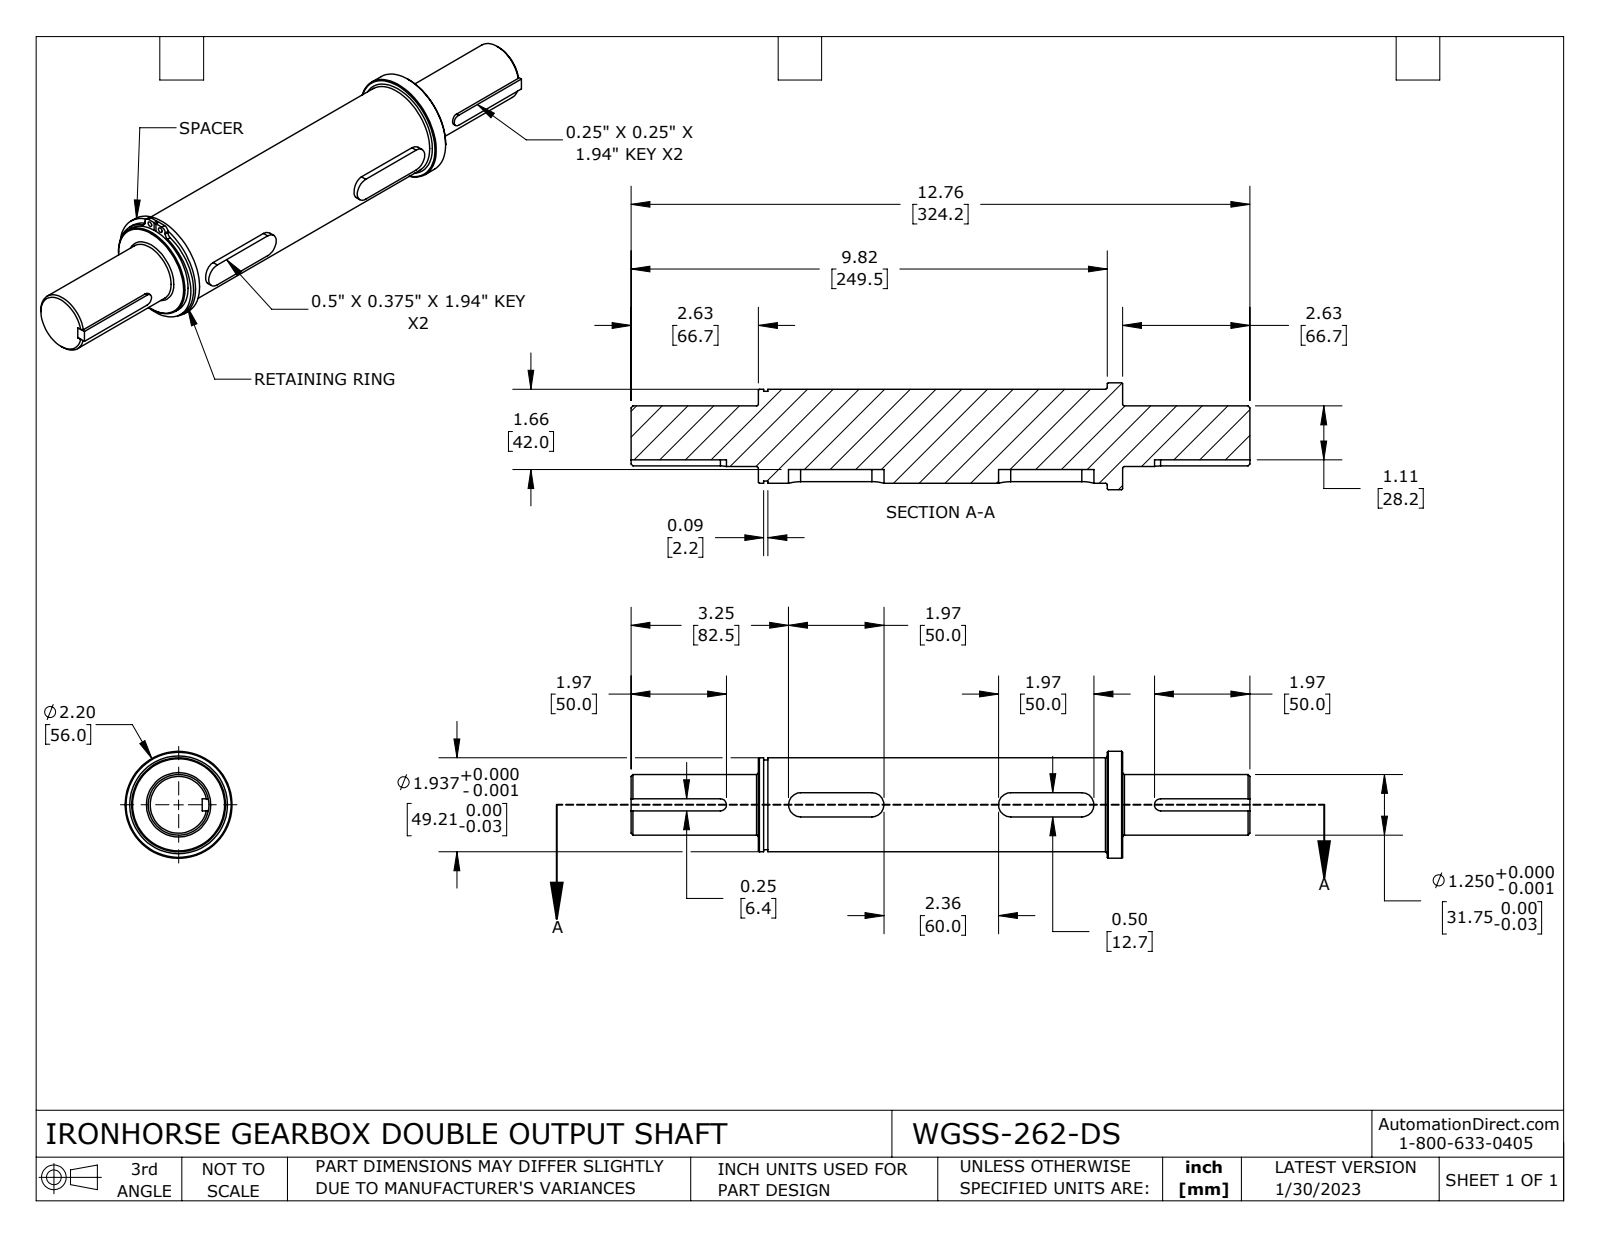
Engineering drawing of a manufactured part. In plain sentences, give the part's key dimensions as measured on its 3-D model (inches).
The part is named "WGSS-262-DS". Its 3-D file was written by "SolidWorks 2021 (CONFIG_CONTROL_DESIGN)". It is 7 solids with 110 faces: 47 planar, 47 cylindrical and 16 other. Overall it measures 12.764 by 2.254 by 2.205 inches. Its volume is 29.31 cubic inches and its surface area 94.72 square inches. Round holes: 2 of diameter 0.106, 1 of diameter 1.799, 1 of diameter 1.945. Round bosses or shafts: 1 of diameter 2.205, 1 of diameter 2.087, 1 of diameter 1.937, 1 of diameter 1.85, 1 of diameter 1.25. Partial cylindrical surfaces (rounded edges, fillets, slot ends): 4 of radius 0.1, 4 of radius 0.25, 2 of radius 0.125. The main face-to-face distances are 0.375, 0.125, 0.197, 2.626, 10.138, 7.315, 0.5, 0.118, 7.512, 0.25. The hole center spacings are 1.063, 0.303.
